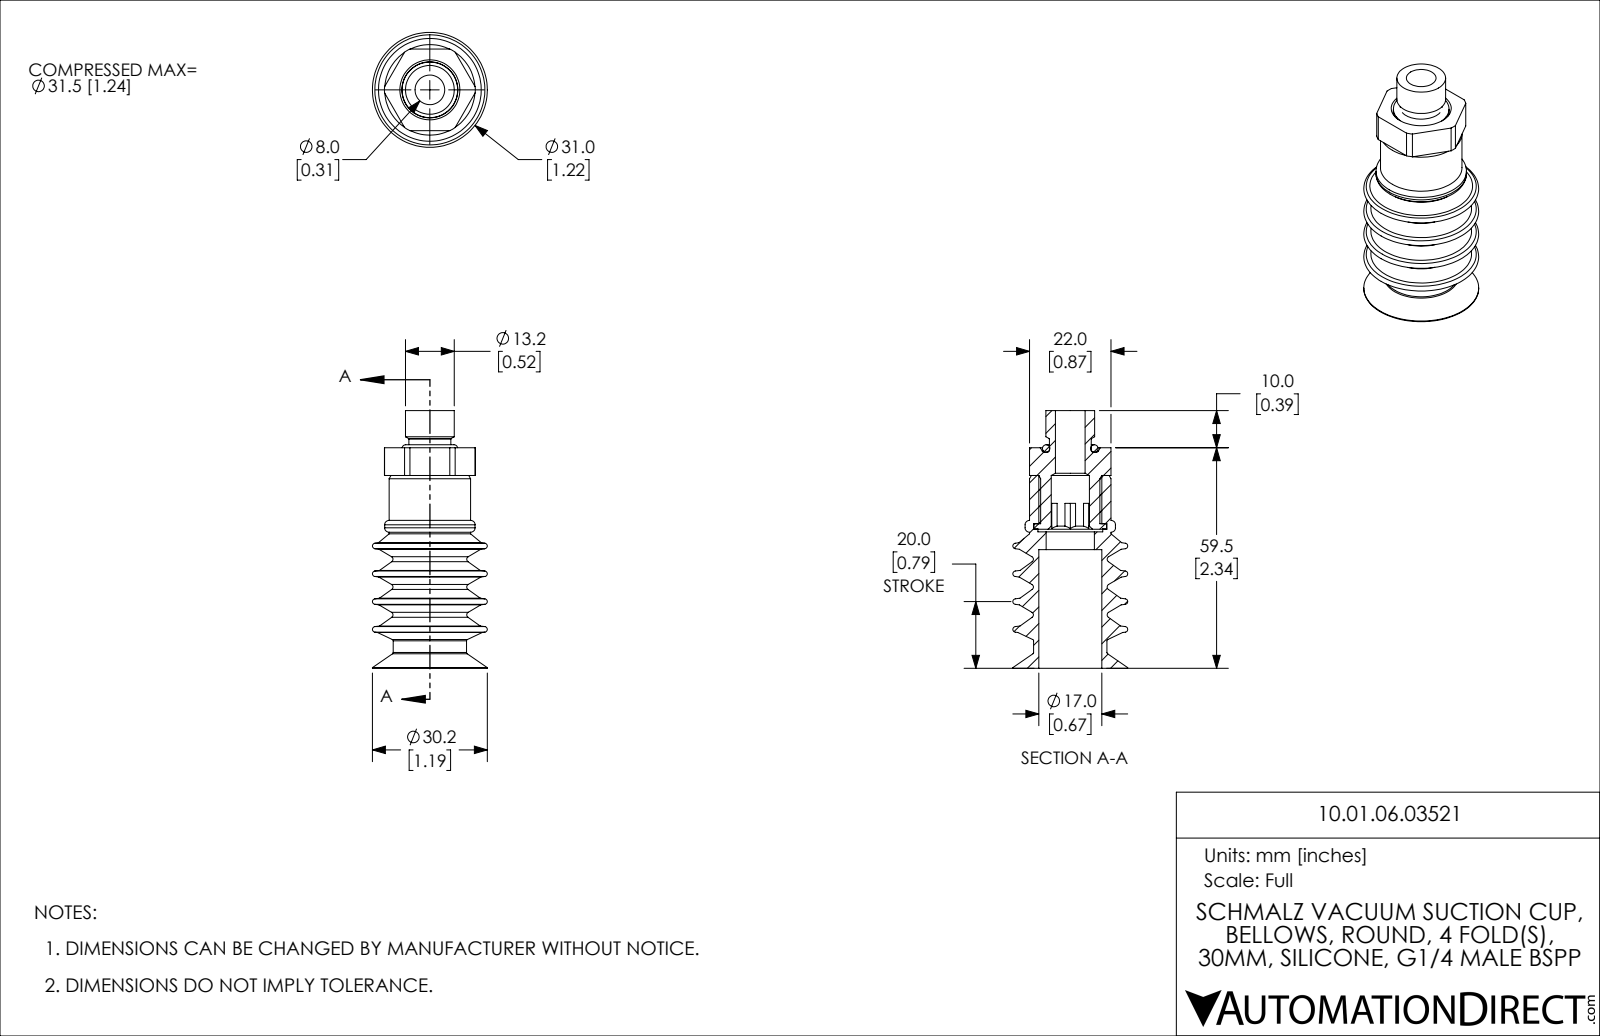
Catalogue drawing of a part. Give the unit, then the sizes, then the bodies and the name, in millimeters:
Units: millimetres
Overall size (bounding box): 69.5 × 31 × 31
Round holes (diameter × count): ⌀8 ×1, ⌀10.3 ×1, ⌀13 ×1, ⌀16 ×1, ⌀17 ×1, ⌀17.5 ×1, ⌀19.6 ×1
Round bosses / shafts (diameter × count): ⌀31 ×1, ⌀24.4 ×1, ⌀22 ×1, ⌀19.8 ×1, ⌀13.16 ×1, ⌀11.3 ×1
Partial cylindrical surfaces — rounded edges, fillets, slot ends (radius × count): R12.25 ×1
Main face-to-face distances: 22, 52, 37.5, 7.5, 59.5, 14.5, 39, 1.5, 13, 20.5
Volume: 18 443 mm³ · Surface area: 14 004 mm²
Bodies: 3 solids, 159 faces (36 planar, 39 cylindrical, 84 other)
Part name (STEP PRODUCT): 10.01.06.03521
STEP written by: SolidWorks 2021 (CONFIG_CONTROL_DESIGN)
